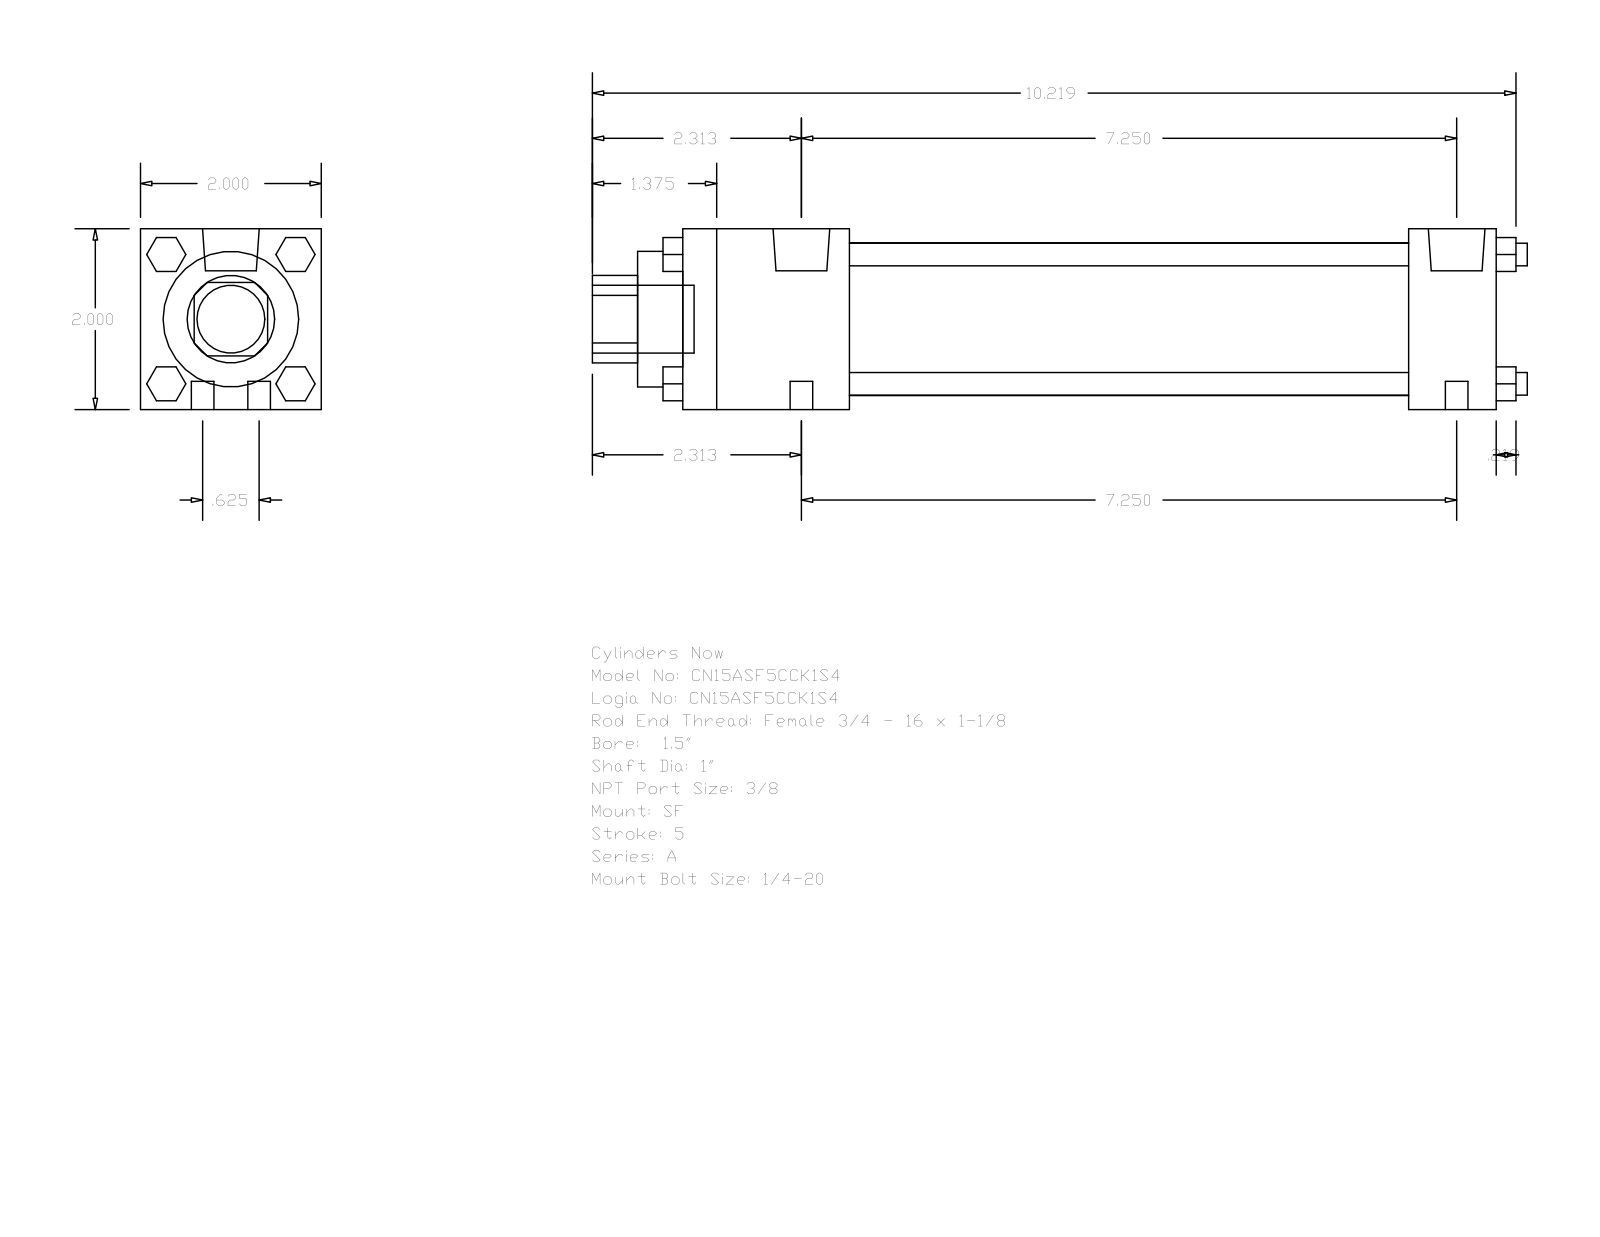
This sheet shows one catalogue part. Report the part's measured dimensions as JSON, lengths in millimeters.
{"part_name": "A_SF__0150_1", "step_written_by": "GSSL Pune (CONFIG_CONTROL_DESIGN)", "units": "millimeters", "bodies": {"solids": 0, "faces": 124, "planar": 94, "cylindrical": 30, "other": 0}, "overall_size": [262.73, 50.8, 50.8], "round_holes": [[25.4, 1], [38.1, 1], [42.93, 1]], "round_bosses_or_shafts": [[6.35, 8], [15.93, 2], [5.56, 2], [19.05, 1]], "partial_cylinders_radius": [[12.29, 1]], "face_to_face_distances": [50.8, 228.6, 46.83, 203.99, 157.16, 181.77, 24.61, 12.7, 59.53, 216.69]}
